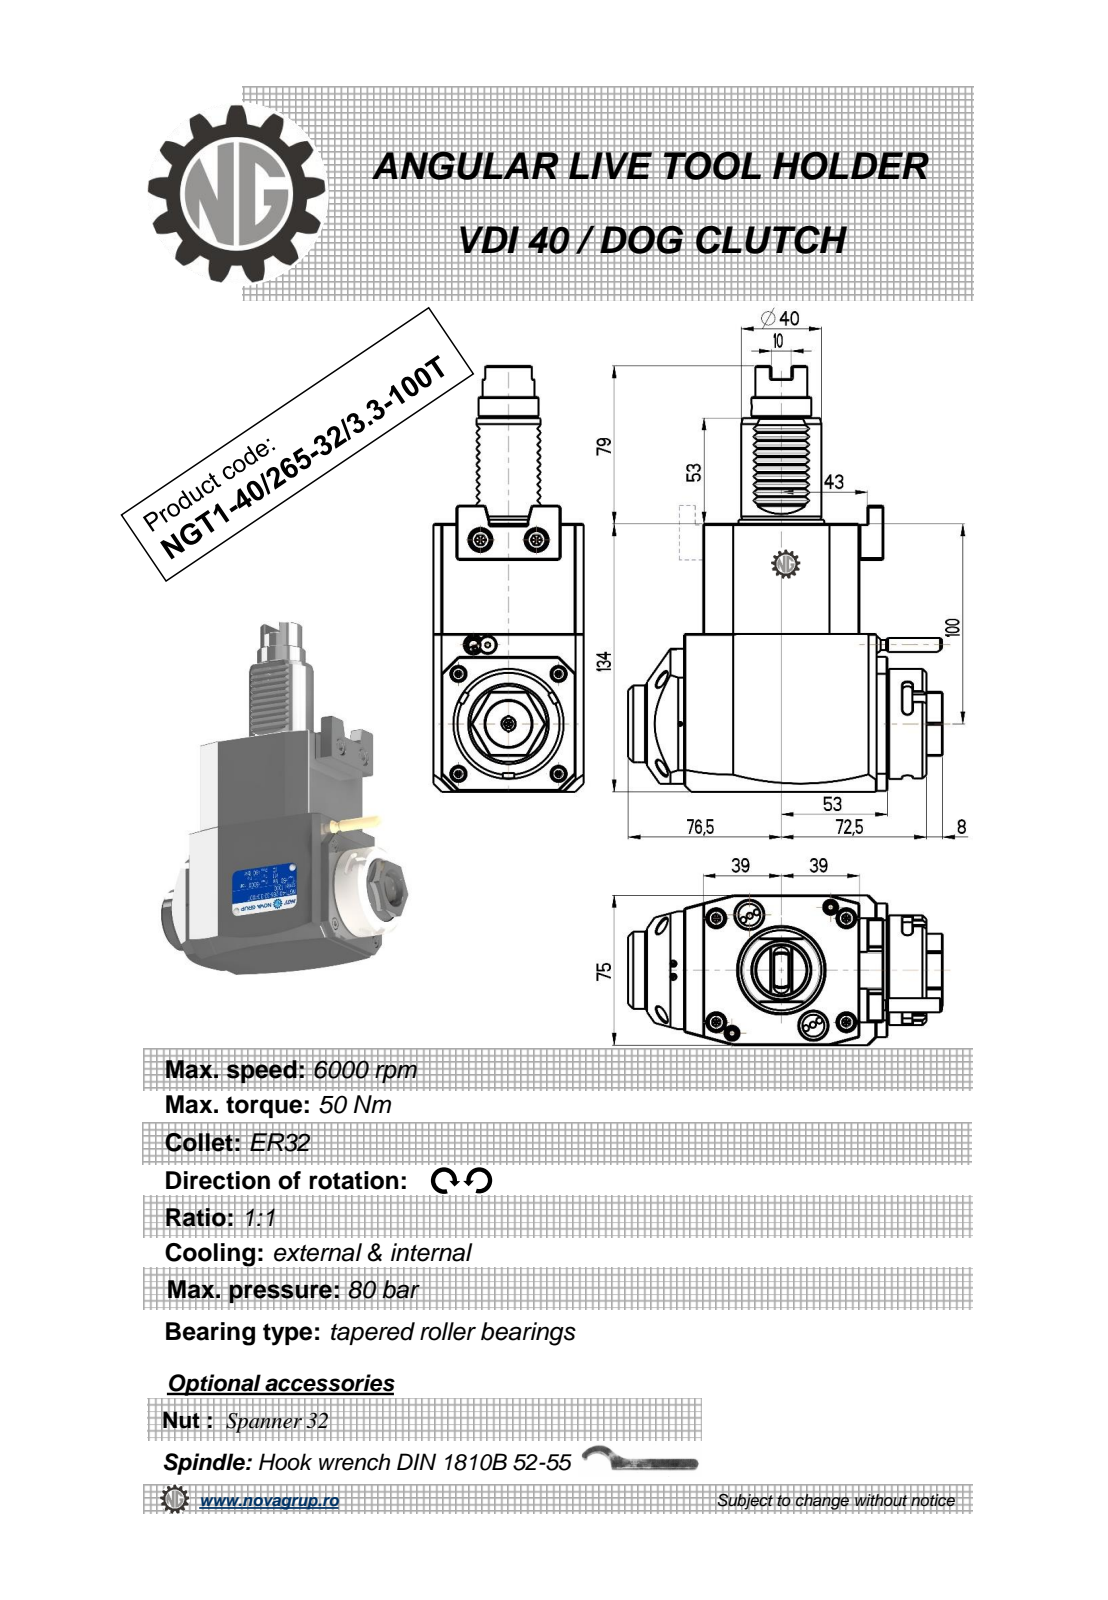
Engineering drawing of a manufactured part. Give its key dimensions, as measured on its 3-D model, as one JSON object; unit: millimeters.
{"part_name": "NGT1_40_265_32_3_3_100T", "step_written_by": "PRO/ENGINEER BY PARAMETRIC TECHNOLOGY CORPORATION, 2010280 (CONFIG_CONTROL_DESIGN)", "units": "millimeters", "bodies": {"solids": 1, "faces": 387, "planar": 245, "cylindrical": 74, "other": 68}, "overall_size": [213, 157, 75], "volume_mm3": 1090000, "surface_area_mm2": 79019, "round_holes": [[2.5, 1], [3, 1], [4.2, 1], [23, 1]], "round_bosses_or_shafts": [[55, 1], [48, 1], [40, 1], [38.5, 1], [30, 1], [26, 1], [8, 1], [7, 1]], "partial_cylinders_radius": [[0.3, 20], [0.26, 6], [2.5, 6], [0.5, 2], [1, 2], [180, 2], [12.5, 1], [24.5, 1]], "face_to_face_distances": [75, 134, 78, 14, 92, 19.5, 84.88, 21.5, 111.5, 33.5], "hole_center_spacings": [43.2, 120.28, 158.5]}
